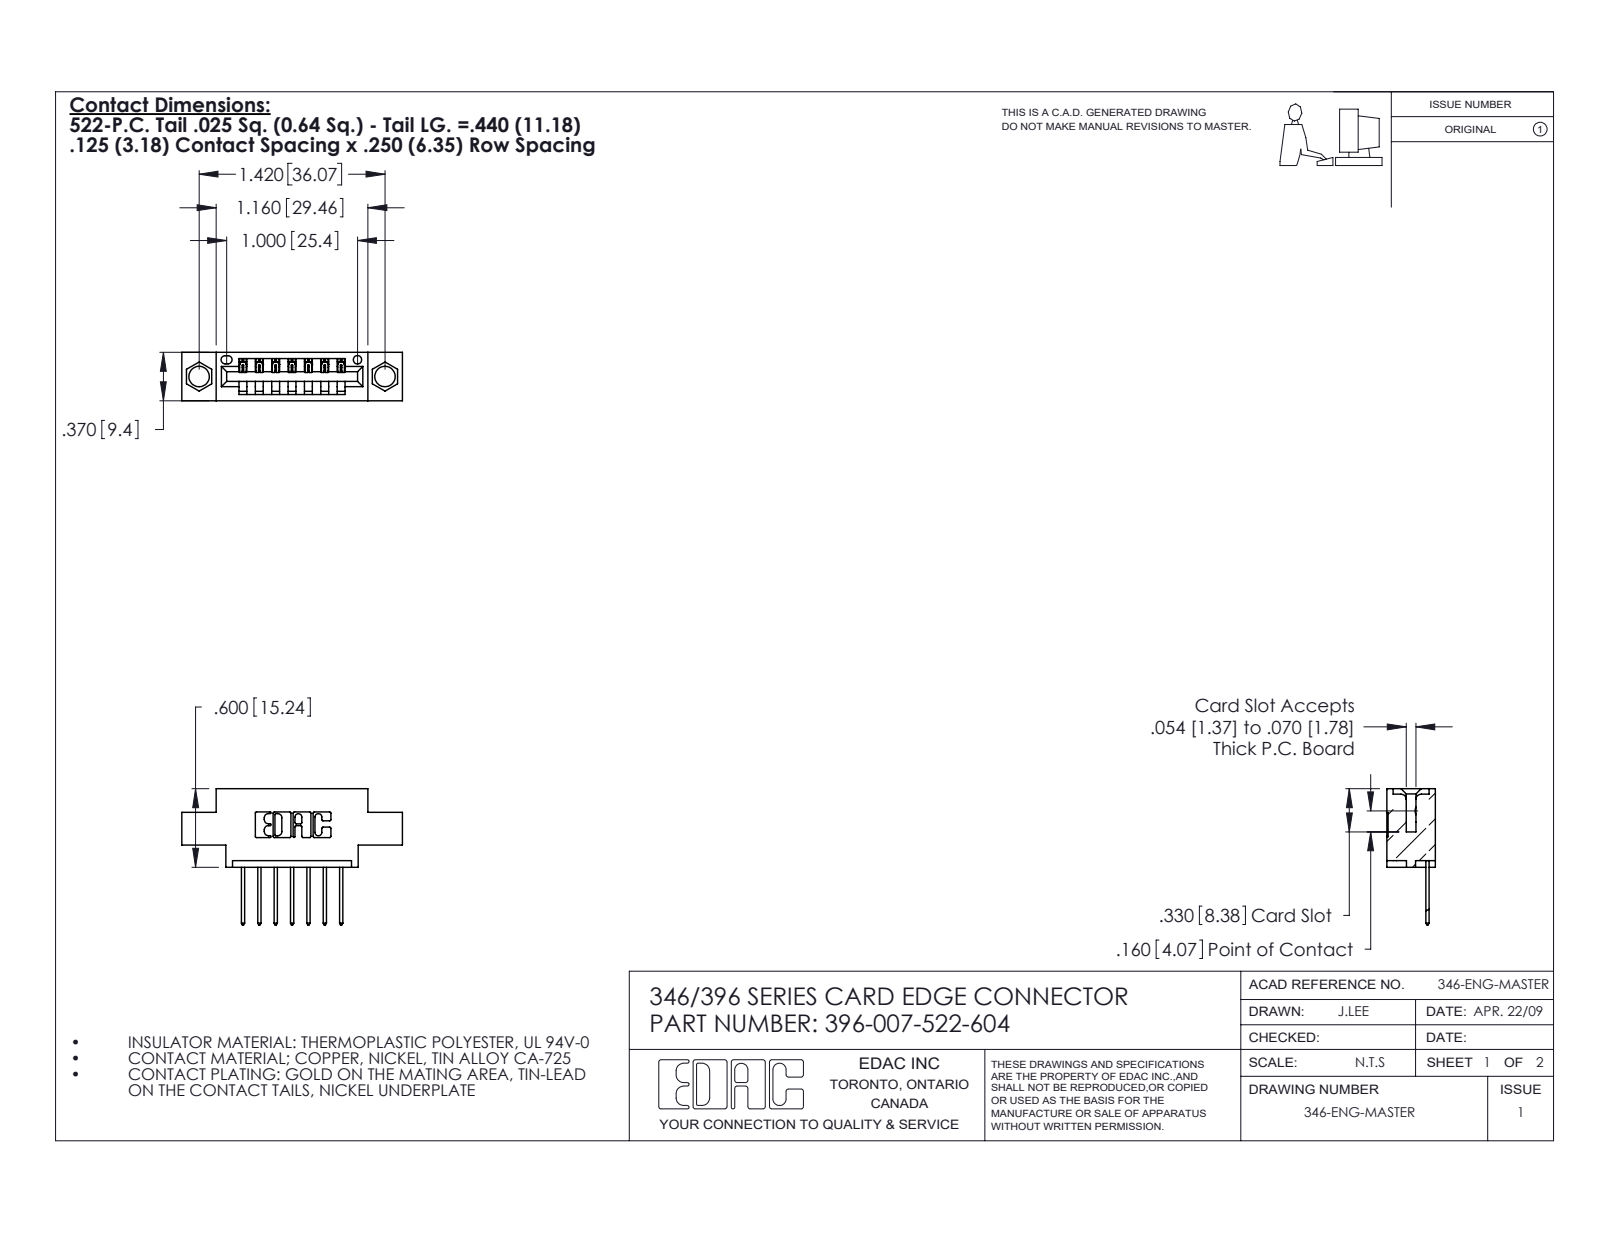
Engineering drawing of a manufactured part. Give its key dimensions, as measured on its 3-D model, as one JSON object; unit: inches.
{"part_name": "345-292-001_345-293-122; 396-007-522-604; 346 Part_0.170 Offset - 0.156 Dia-TH", "step_written_by": "SolidWorks 2020 (CONFIG_CONTROL_DESIGN)", "units": "inches", "bodies": {"solids": 8, "faces": 546, "planar": 374, "cylindrical": 172, "other": 0}, "overall_size": [1.685, 1.04, 0.37], "volume_in3": 0.219, "surface_area_in2": 6.417, "round_holes": [[0.156, 2], [0.064, 1]], "partial_cylinders_radius": [[0.01, 22], [0.006, 14], [0.01, 14], [0.007, 6], [0.031, 6], [0.026, 3], [0.031, 2], [0.04, 2]], "face_to_face_distances": [0.25, 0.37, 0.048, 0.322, 0.222, 0.072, 0.298, 0.025, 0.148, 0.1], "hole_center_spacings": [0.246, 1.217, 1.42]}
